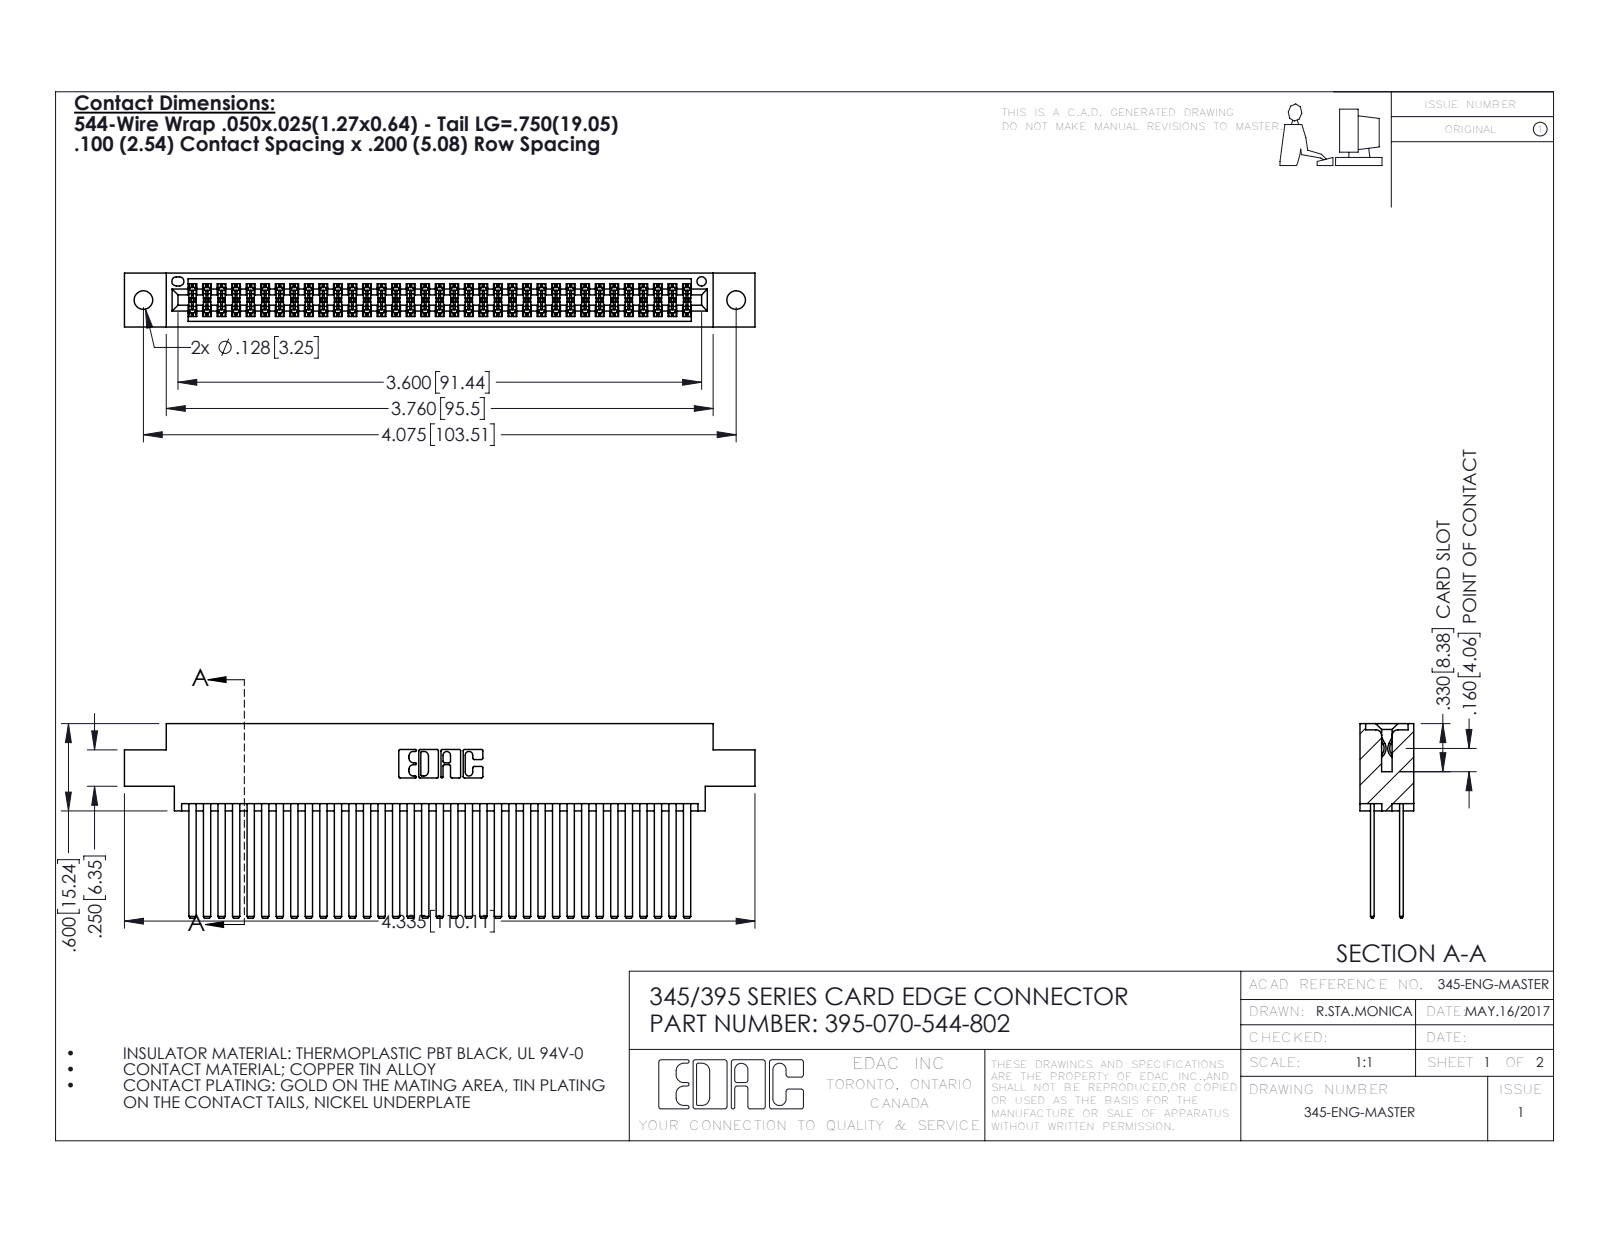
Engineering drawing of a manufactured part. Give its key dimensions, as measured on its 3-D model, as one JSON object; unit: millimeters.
{"part_name": "395-070-544-802; 345-292-001_345-293-144; 345 Part_0.170 Offset - 0.128 Dia", "step_written_by": "SolidWorks 2016 (CONFIG_CONTROL_DESIGN)", "units": "millimeters", "bodies": {"solids": 71, "faces": 3210, "planar": 2114, "cylindrical": 1096, "other": 0}, "overall_size": [110.1, 34, 9.4], "volume_mm3": 11500, "surface_area_mm2": 19550, "round_holes": [[3.3, 2], [1.6, 1]], "partial_cylinders_radius": [[0.2, 105], [0.3, 22], [0.2, 6], [0.8, 6], [0.7, 3], [0.4, 2], [0.5, 2], [0.6, 2]], "face_to_face_distances": [5.1, 0.6, 7.6, 1.8, 2.5, 6.9, 5.7, 4.4, 9.4, 3.8], "hole_center_spacings": [6.9, 97.5, 103.5]}
